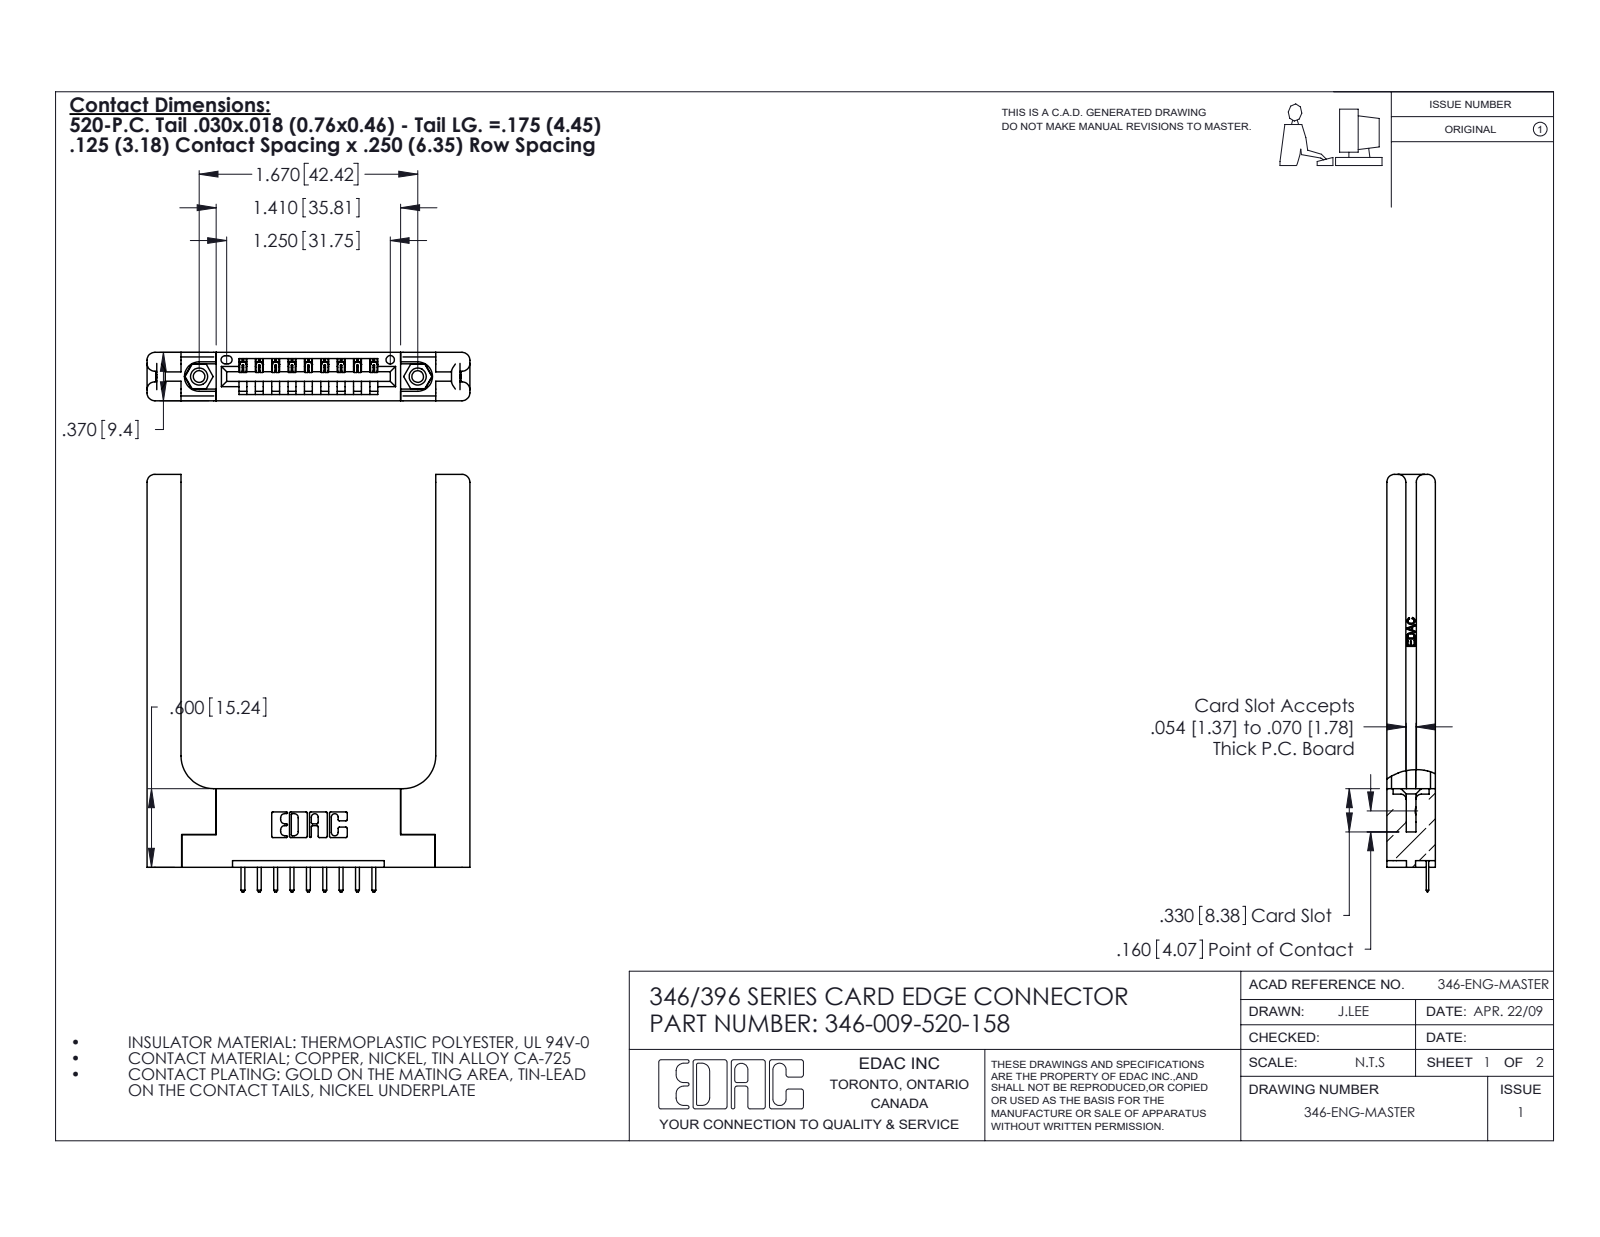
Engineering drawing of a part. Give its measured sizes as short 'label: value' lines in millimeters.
name: 346 Part_Flush Mounting Lugs - 0.156 Dia-TH; 345-250-001_345-250-001-102; 346-009-520-158; 345-292-001_345-293-120 (+1 more)
written by: SolidWorks 2020 (CONFIG_CONTROL_DESIGN)
unit: mm
bodies: 14 solids, 950 faces (616 planar, 274 cylindrical, 60 other)
size: 81 × 62.6 × 9.4
volume: 13 200 mm³; area: 11 920 mm²
holes: 2× ⌀2.3, 2× ⌀3.2, 2× ⌀4, 1× ⌀1.6
bosses: 2× ⌀3.9
rounds: 22× R0.3, 20× R0.3, 18× R0.2, 16× R1.5, 6× R0.2, 6× R0.8, 3× R0.7, 2× R0.8
face distances: 9.4, 3.8, 5.6, 1.8, 3.8, 6.4, 2.6, 1.2, 8.2, 4.4
hole spacings: 6.2, 37.2, 42.4
